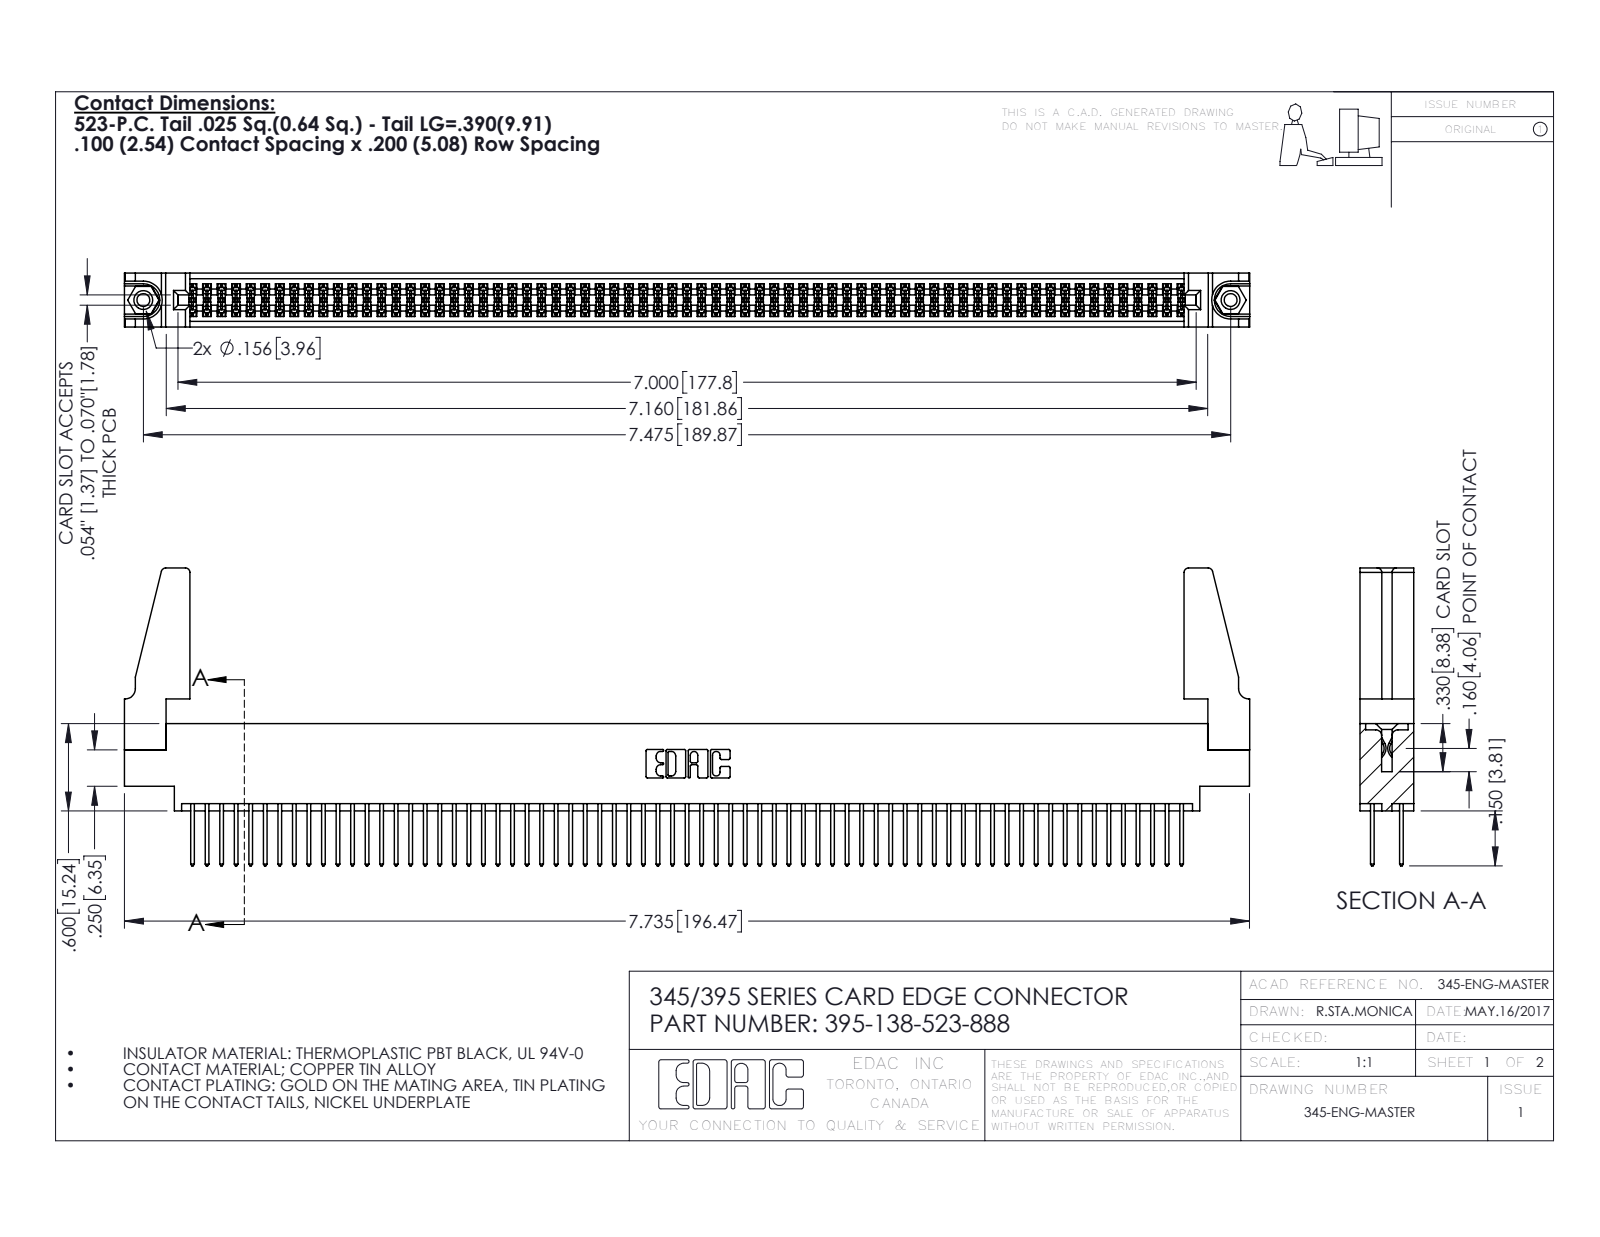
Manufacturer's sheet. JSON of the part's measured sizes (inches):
{"part_name": "345 Part_0.170 Offset - 0.156 Dia-TH; 345-292-001_345-293-123; 345-220-078_345-220-088; 345-250-001_345-250-001-102 (+1 more)", "step_written_by": "SolidWorks 2016 (CONFIG_CONTROL_DESIGN)", "units": "inches", "bodies": {"solids": 143, "faces": 7154, "planar": 4710, "cylindrical": 2428, "other": 16}, "overall_size": [7.736, 2.047, 0.37], "volume_in3": 1.389, "surface_area_in2": 52.53, "round_holes": [[0.089, 2], [0.125, 2], [0.156, 2], [0.064, 1]], "round_bosses_or_shafts": [[0.155, 2]], "partial_cylinders_radius": [[0.006, 207], [0.01, 138], [0.01, 22], [0.03, 8], [0.007, 6], [0.031, 6], [0.026, 3], [0.014, 2]], "face_to_face_distances": [0.072, 0.298, 0.37, 0.098, 0.272, 0.025, 0.2, 0.225, 0.175, 0.149], "hole_center_spacings": [0.27, 7.239, 7.475]}
